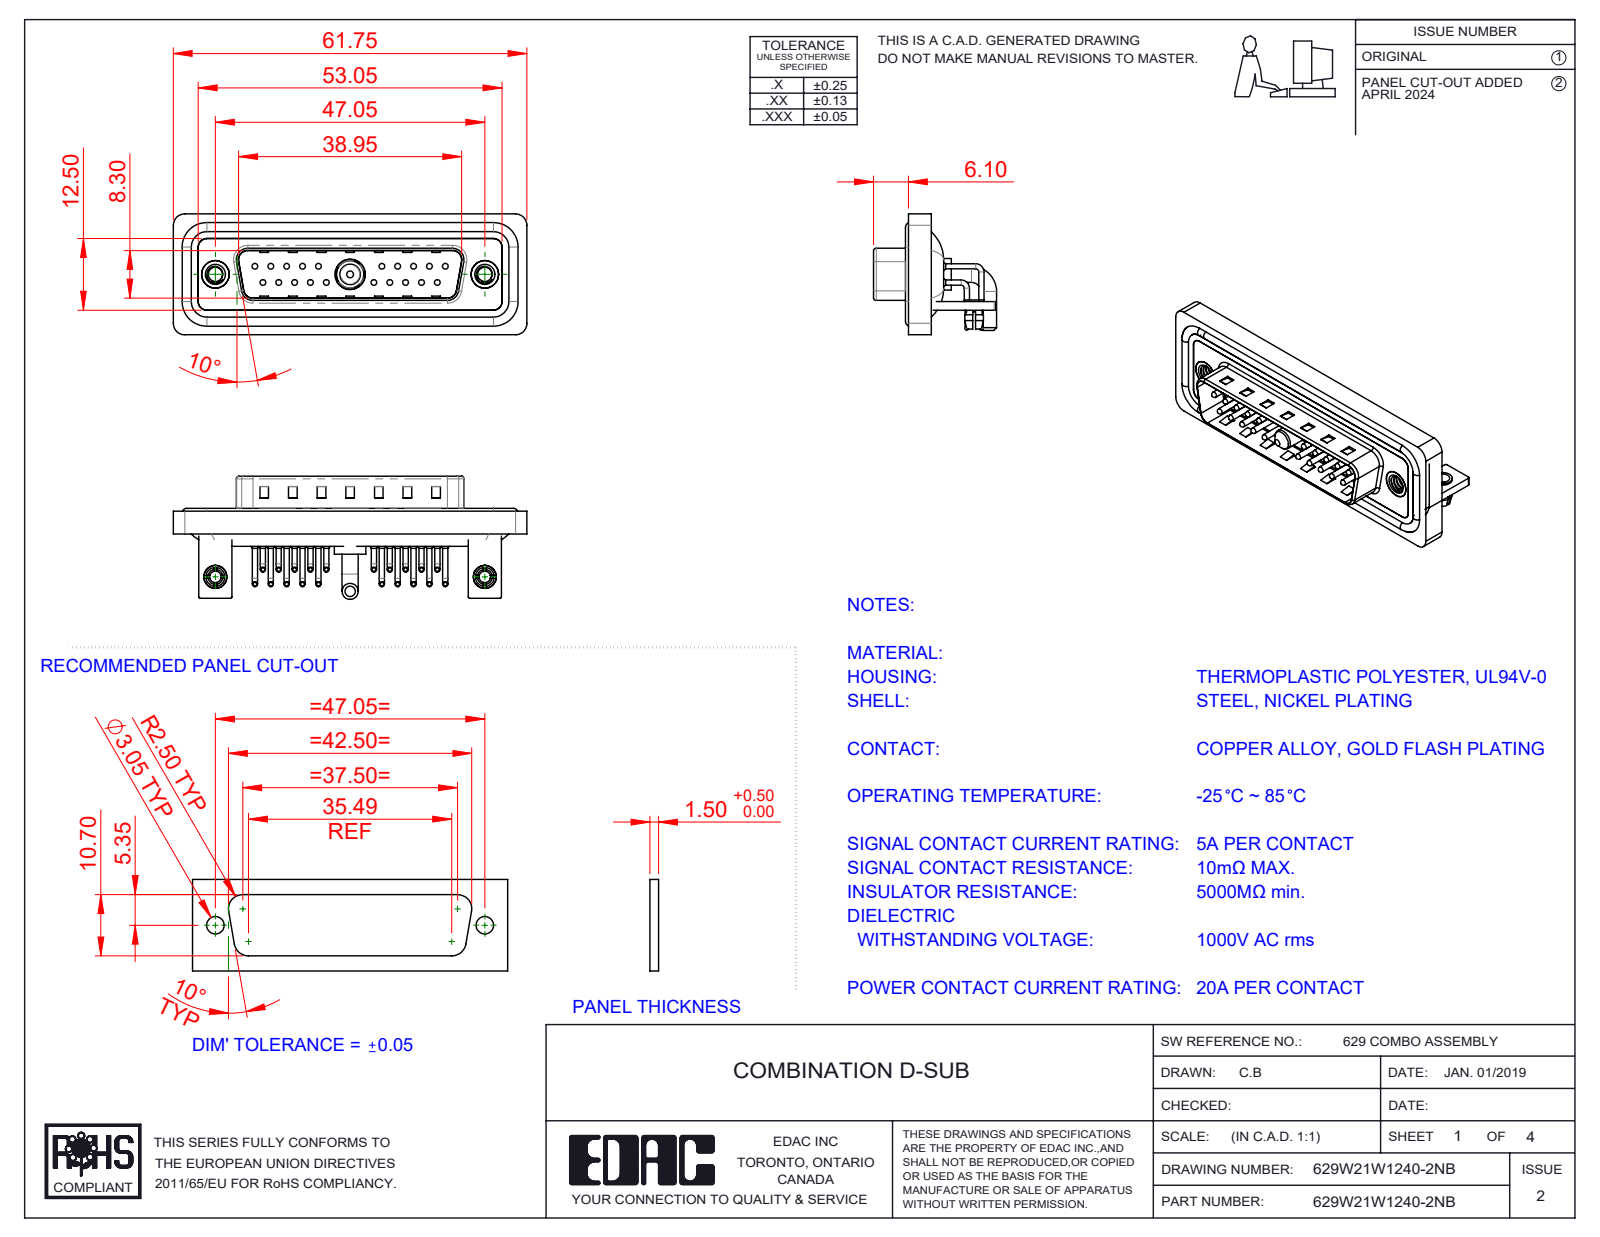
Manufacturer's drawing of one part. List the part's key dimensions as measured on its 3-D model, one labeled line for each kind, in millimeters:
Part name (STEP PRODUCT): 629Combo Contact Row 1; 629Combo Shell Rear_25 Contacts; 629Combo Contact Row 2; 629W21W1240-2NB (+7 more)
STEP written by: SolidWorks 2023 (CONFIG_CONTROL_DESIGN)
Units: millimetres
Bodies: 33 solids, 2856 faces (1567 planar, 979 cylindrical, 310 other)
Overall size (bounding box): 61.75 × 21.5 × 21.1
Volume: 7 726 mm³ · Surface area: 13 519 mm²
Round holes (diameter × count): ⌀2 ×22, ⌀0.75 ×20, ⌀1.6 ×20, ⌀2.5 ×4, ⌀3.2 ×2, ⌀4 ×2, ⌀4.8 ×2, ⌀5 ×2, ⌀4.85 ×1, ⌀5.3 ×1
Round bosses / shafts (diameter × count): ⌀0.9 ×40, ⌀1.5 ×20, ⌀1 ×20, ⌀0.65 ×20, ⌀1.6 ×4, ⌀4.9 ×2, ⌀4 ×2, ⌀3.4 ×2
Partial cylindrical surfaces — rounded edges, fillets, slot ends (radius × count): R1.01 ×20, R2 ×19, R1.5 ×18, R0.25 ×16, R0.5 ×9, R1.6 ×8, R0.6 ×4, R0.65 ×4
Main face-to-face distances: 0.4, 0.8, 2.1, 2.9, 1.5, 1.1, 4.1, 1.6, 4.5, 3.7
Hole centre spacings: 3.16, 2.77, 5.54, 8.31, 5.04, 19.39, 20.97, 22.16
